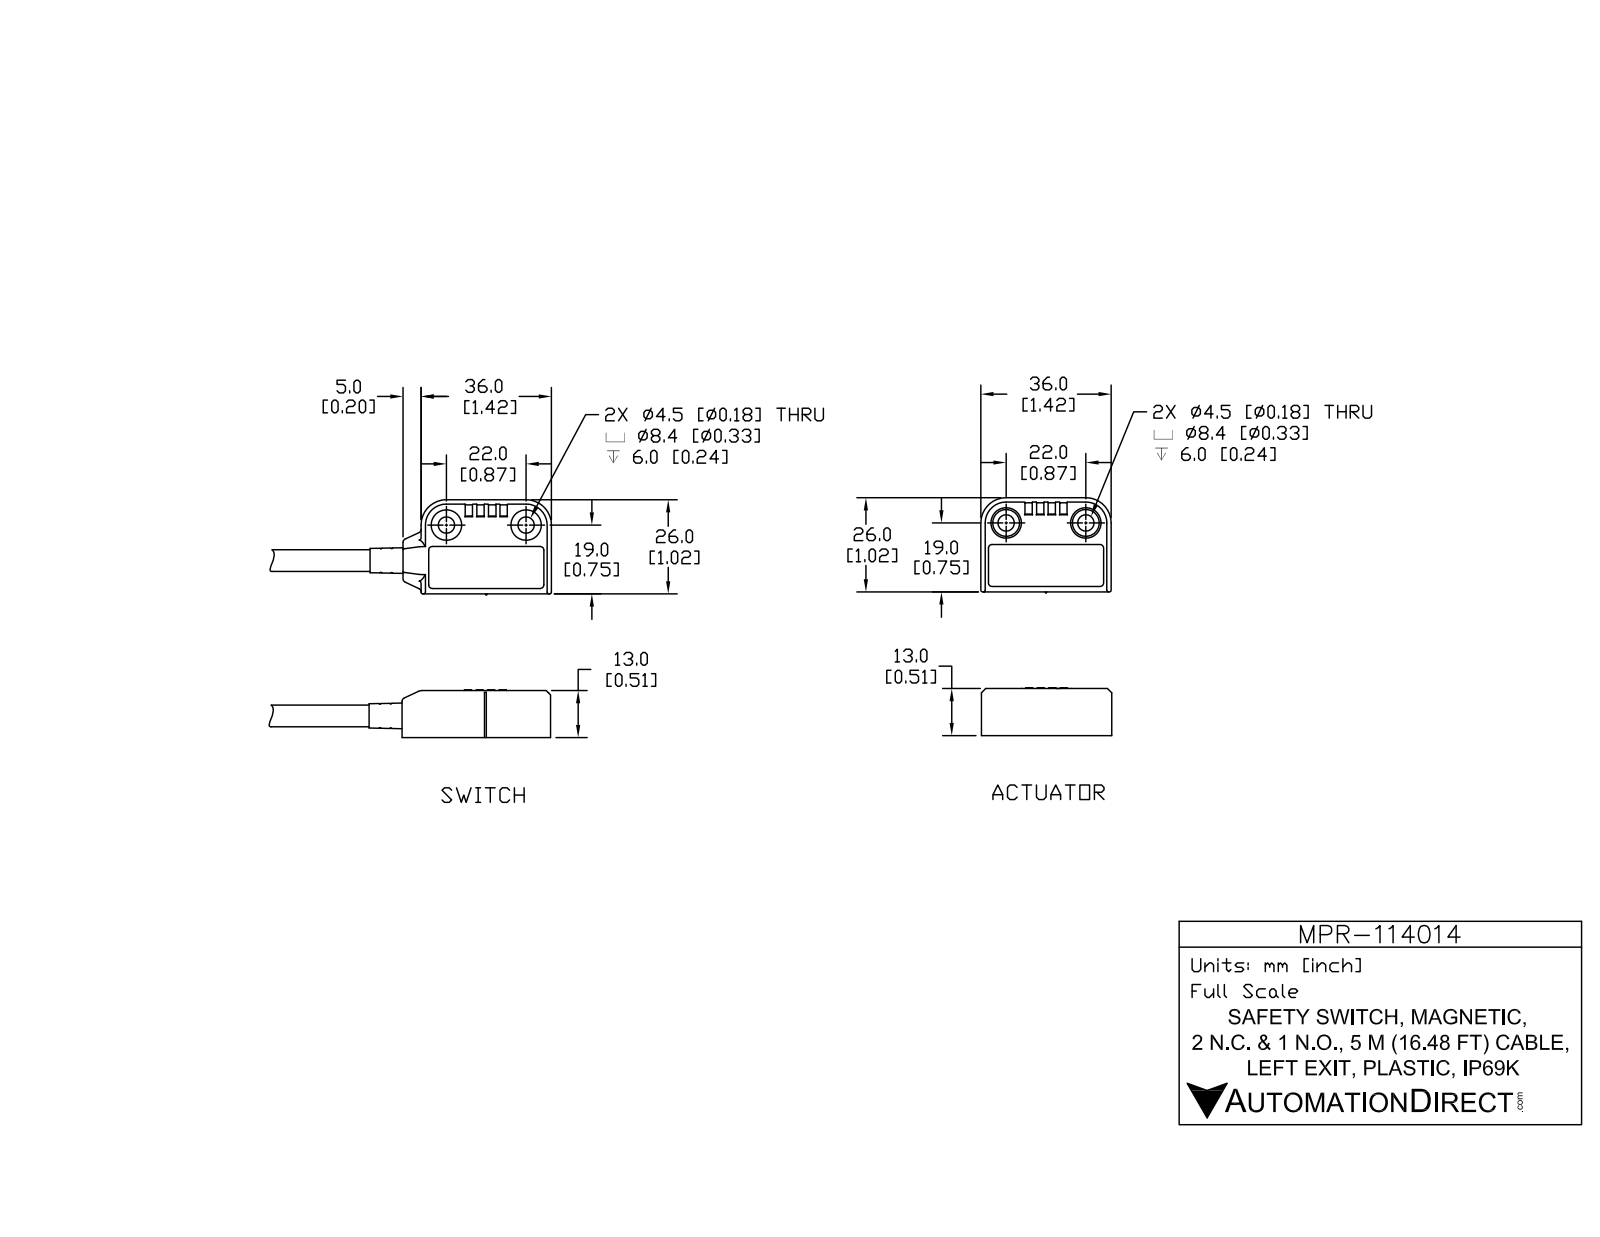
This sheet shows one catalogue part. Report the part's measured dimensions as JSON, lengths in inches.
{"part_name": "MPR-114014_1; MPR-114014; MPR-114014_2", "step_written_by": "SolidWorks 2017 (AUTOMOTIVE_DESIGN)", "units": "inches", "bodies": {"solids": 9, "faces": 1116, "planar": 493, "cylindrical": 327, "other": 296}, "overall_size": [7.658, 2.087, 0.528], "volume_in3": 1.059, "surface_area_in2": 29.57, "round_holes": [[0.177, 4], [0.331, 4], [0.195, 2], [0.197, 1], [0.232, 1], [0.276, 1]], "round_bosses_or_shafts": [[0.079, 3], [0.197, 2], [0.091, 2], [0.339, 1], [0.299, 1], [0.28, 1], [0.236, 1]], "partial_cylinders_radius": [[0.02, 85], [0.008, 30], [0.012, 28], [0.004, 17], [0.039, 13], [0.169, 4], [0.201, 4], [0.276, 4]], "face_to_face_distances": [0.055, 0.461, 0.39, 0.453, 0.047, 1.063, 0.059, 0.094, 0.445, 0.031], "hole_center_spacings": [0.866, 0.445, 0.974, 1.091, 1.393, 1.535, 1.763, 0.396]}
